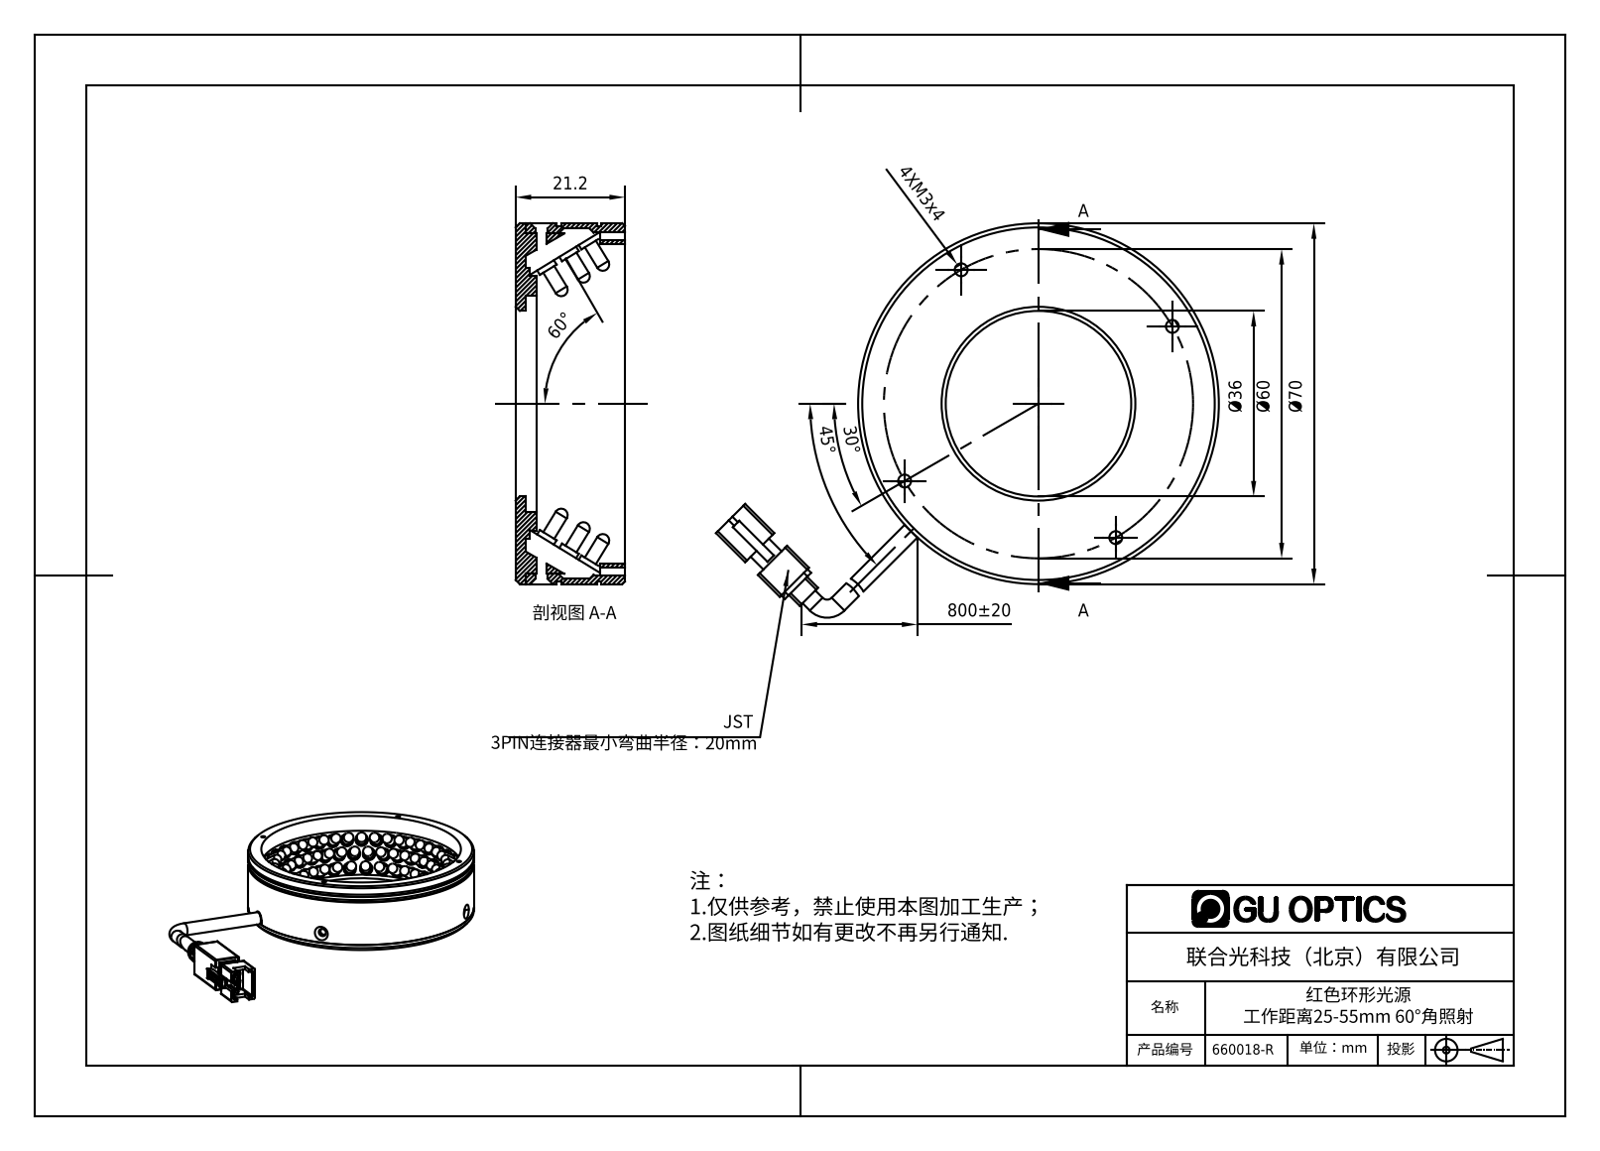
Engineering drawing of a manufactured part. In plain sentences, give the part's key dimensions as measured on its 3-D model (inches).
The part is named "660018-R". Its 3-D file was written by "SolidWorks 2016 (AUTOMOTIVE_DESIGN)". It is 118 solids with 2275 faces: 1503 planar, 596 cylindrical and 176 other. Overall it measures 4.83 by 3.181 by 0.892 inches. Its volume is 1.665 cubic inches and its surface area 58.26 square inches. Round holes: 4 of diameter 0.049, 4 of diameter 0.098, 3 of diameter 0.15, 2 of diameter 0.079, 2 of diameter 0.094, 1 of diameter 1.417, 1 of diameter 1.654, 1 of diameter 2.441, 1 of diameter 2.598, 1 of diameter 2.677. Round bosses or shafts: 112 of diameter 0.15, 112 of diameter 0.118, 1 of diameter 2.756, 1 of diameter 2.717, 1 of diameter 2.067, 1 of diameter 1.949, 1 of diameter 0.138. Partial cylindrical surfaces (rounded edges, fillets, slot ends): 15 of radius 0.004, 13 of radius 0.008, 12 of radius 0.016, 1 of radius 0.012, 1 of radius 0.027, 1 of radius 0.055, 1 of radius 0.065, 1 of radius 0.177. The main face-to-face distances are 0.079, 0.039, 0.835, 0.756, 0.02, 0.106, 0.028, 0.728, 0.059, 0.535. The hole center spacings are 0.644, 1.181, 1.233, 1.28, 1.67, 1.809, 2.131, 2.377.
